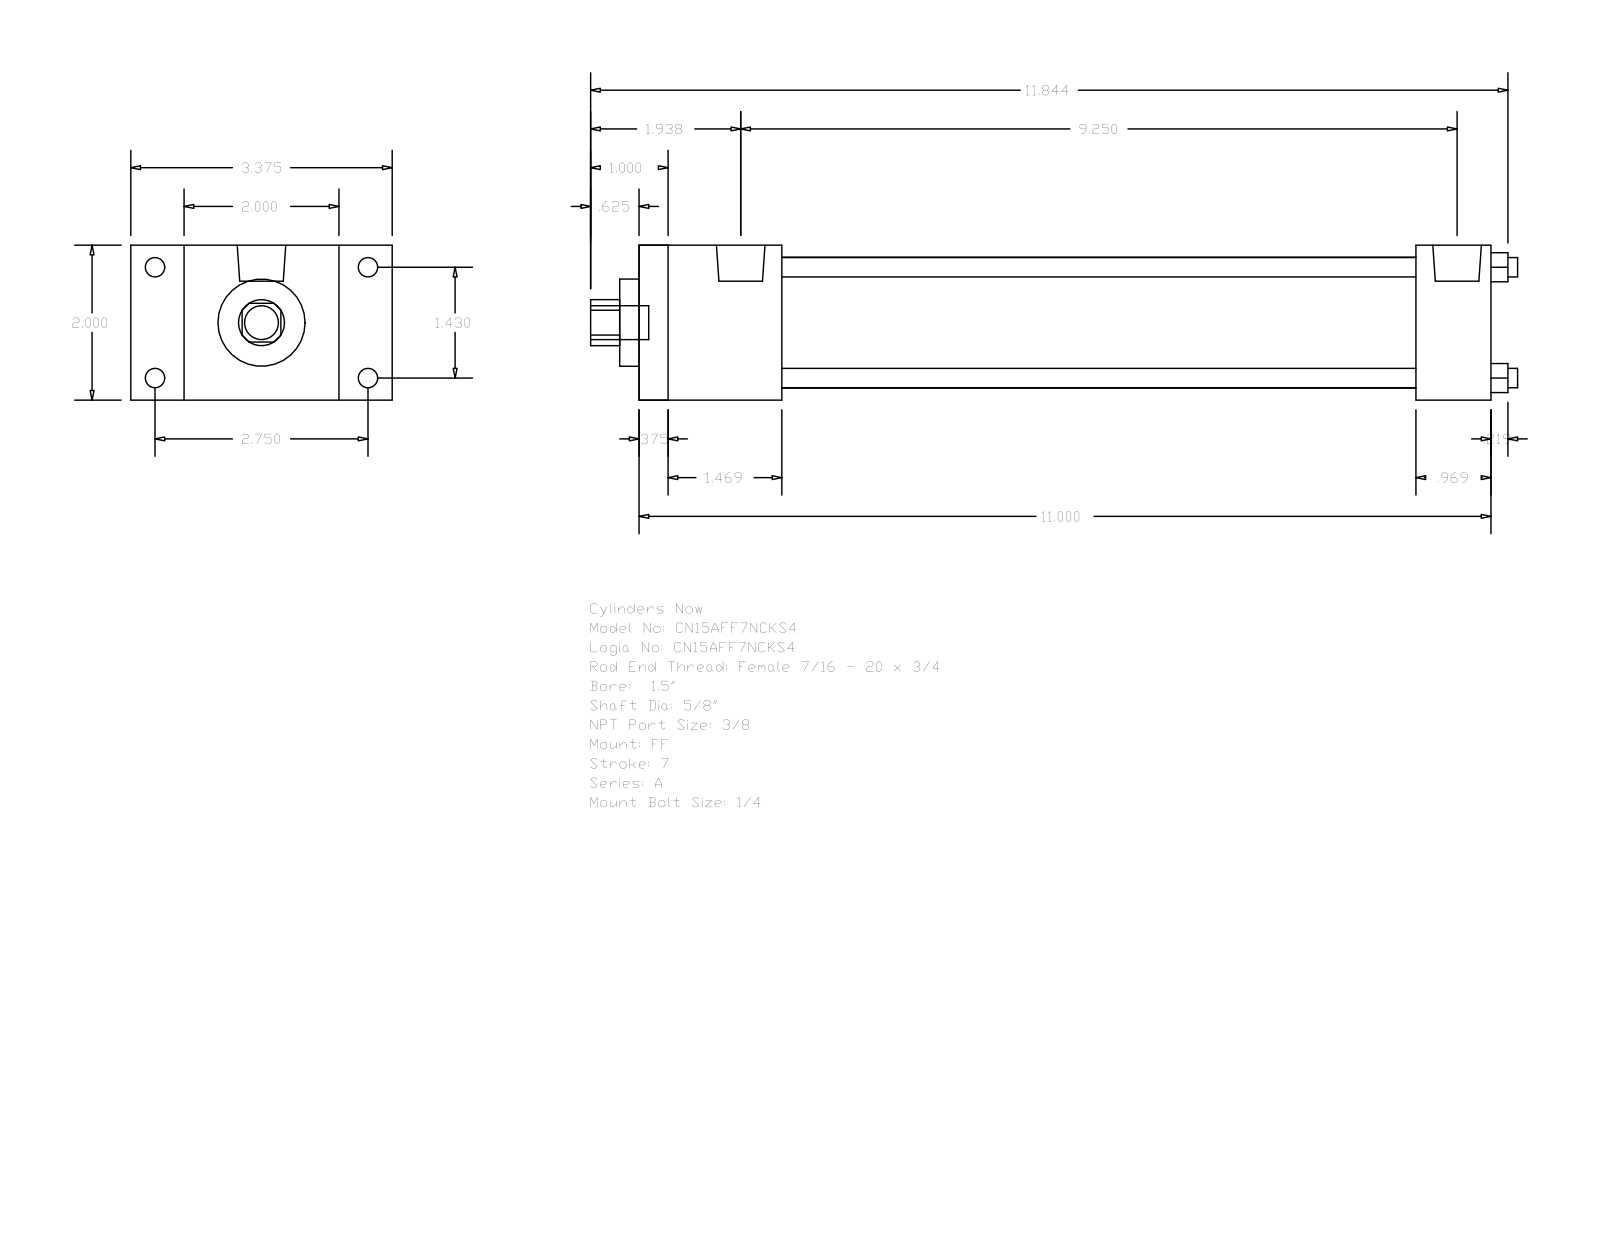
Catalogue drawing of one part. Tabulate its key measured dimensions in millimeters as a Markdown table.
| quantity | value |
| --- | --- |
| part name | A_FF__0150_0.625 |
| STEP written by | GSSL Pune (CONFIG_CONTROL_DESIGN) |
| units | millimeters |
| bodies | 0 solids, 92 faces (64 planar, 28 cylindrical, 0 other) |
| overall size | 304.01 × 85.72 × 50.8 |
| round holes (diameter × count) | 6.35 × 4, 15.88 × 1, 28.57 × 1, 42.93 × 1 |
| round bosses / shafts (diameter × count) | 6.35 × 4, 5.56 × 4, 15.93 × 2, 11.11 × 1 |
| partial cylindrical surfaces (radius × count) | 7.54 × 1 |
| main face-to-face distances | 50.8, 279.39, 9.52, 269.87, 46.83, 254.79, 37.31, 245.27, 207.96, 232.56 |
| hole center spacings | 25.68, 36.32, 51.36 |
